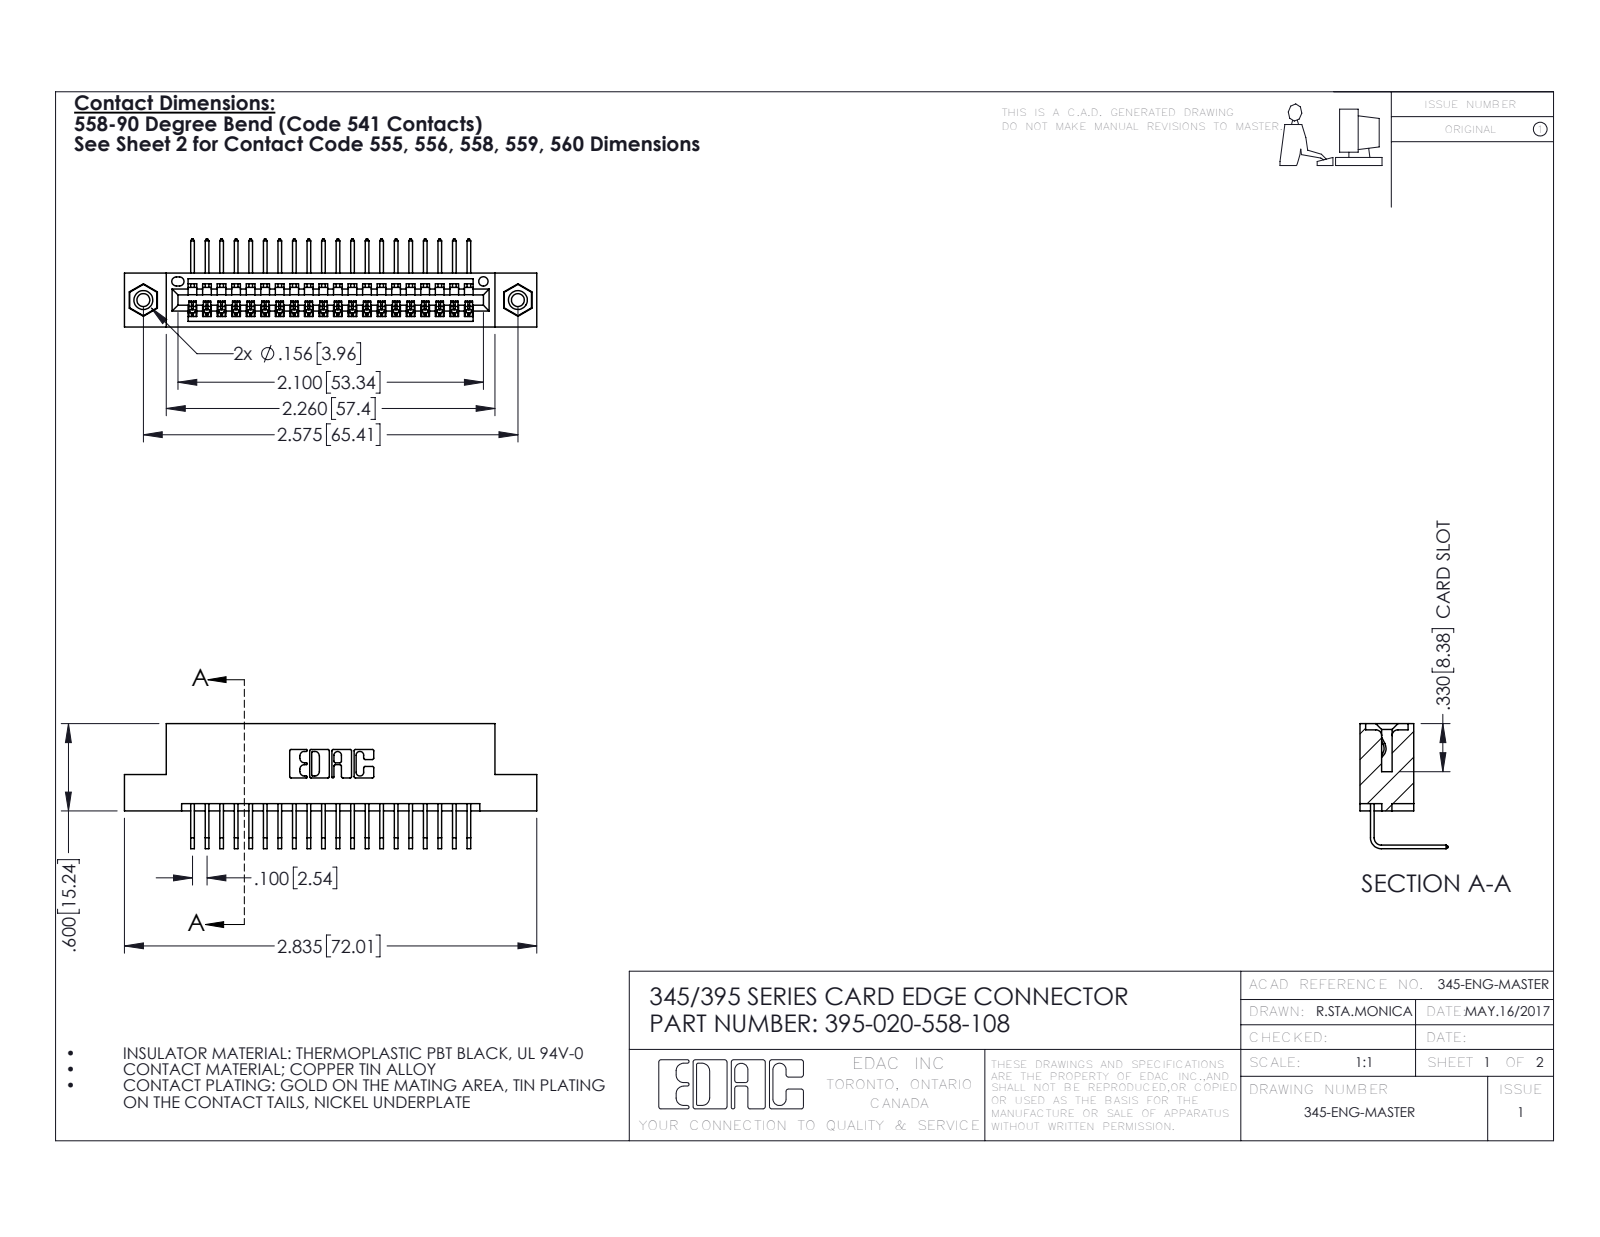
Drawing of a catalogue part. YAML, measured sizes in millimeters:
part_name: "395-020-558-108; 345 Part_Flush Mounting Lugs - 0.156 Dia-TI; 345-292-001_558 Tail - 2; 345-250-001_345-250-003-102"
step_written_by: "SolidWorks 2016 (CONFIG_CONTROL_DESIGN)"
units: millimeters
bodies: {solids: 23, faces: 1386, planar: 952, cylindrical: 418, other: 16}
overall_size: [72, 21.8, 15.4]
volume: 6720
surface_area: 9039
round_holes:
  - {diameter: 2.3, count: 2}
  - {diameter: 3.2, count: 2}
  - {diameter: 4, count: 2}
  - {diameter: 1.6, count: 1}
round_bosses_or_shafts:
  - {diameter: 3.9, count: 2}
partial_cylinders:
  - {radius: 0.2, count: 40}
  - {radius: 0.3, count: 22}
  - {radius: 0.2, count: 6}
  - {radius: 0.8, count: 6}
  - {radius: 0.7, count: 3}
  - {radius: 0.8, count: 2}
  - {radius: 1, count: 2}
  - {radius: 0.4, count: 1}
face_to_face_distances: [1.8, 7.6, 5.1, 9.4, 2.5, 6.9, 0.6, 5.7, 3.8, 15.2]
hole_center_spacings: [6.9, 59.5, 65.4]
